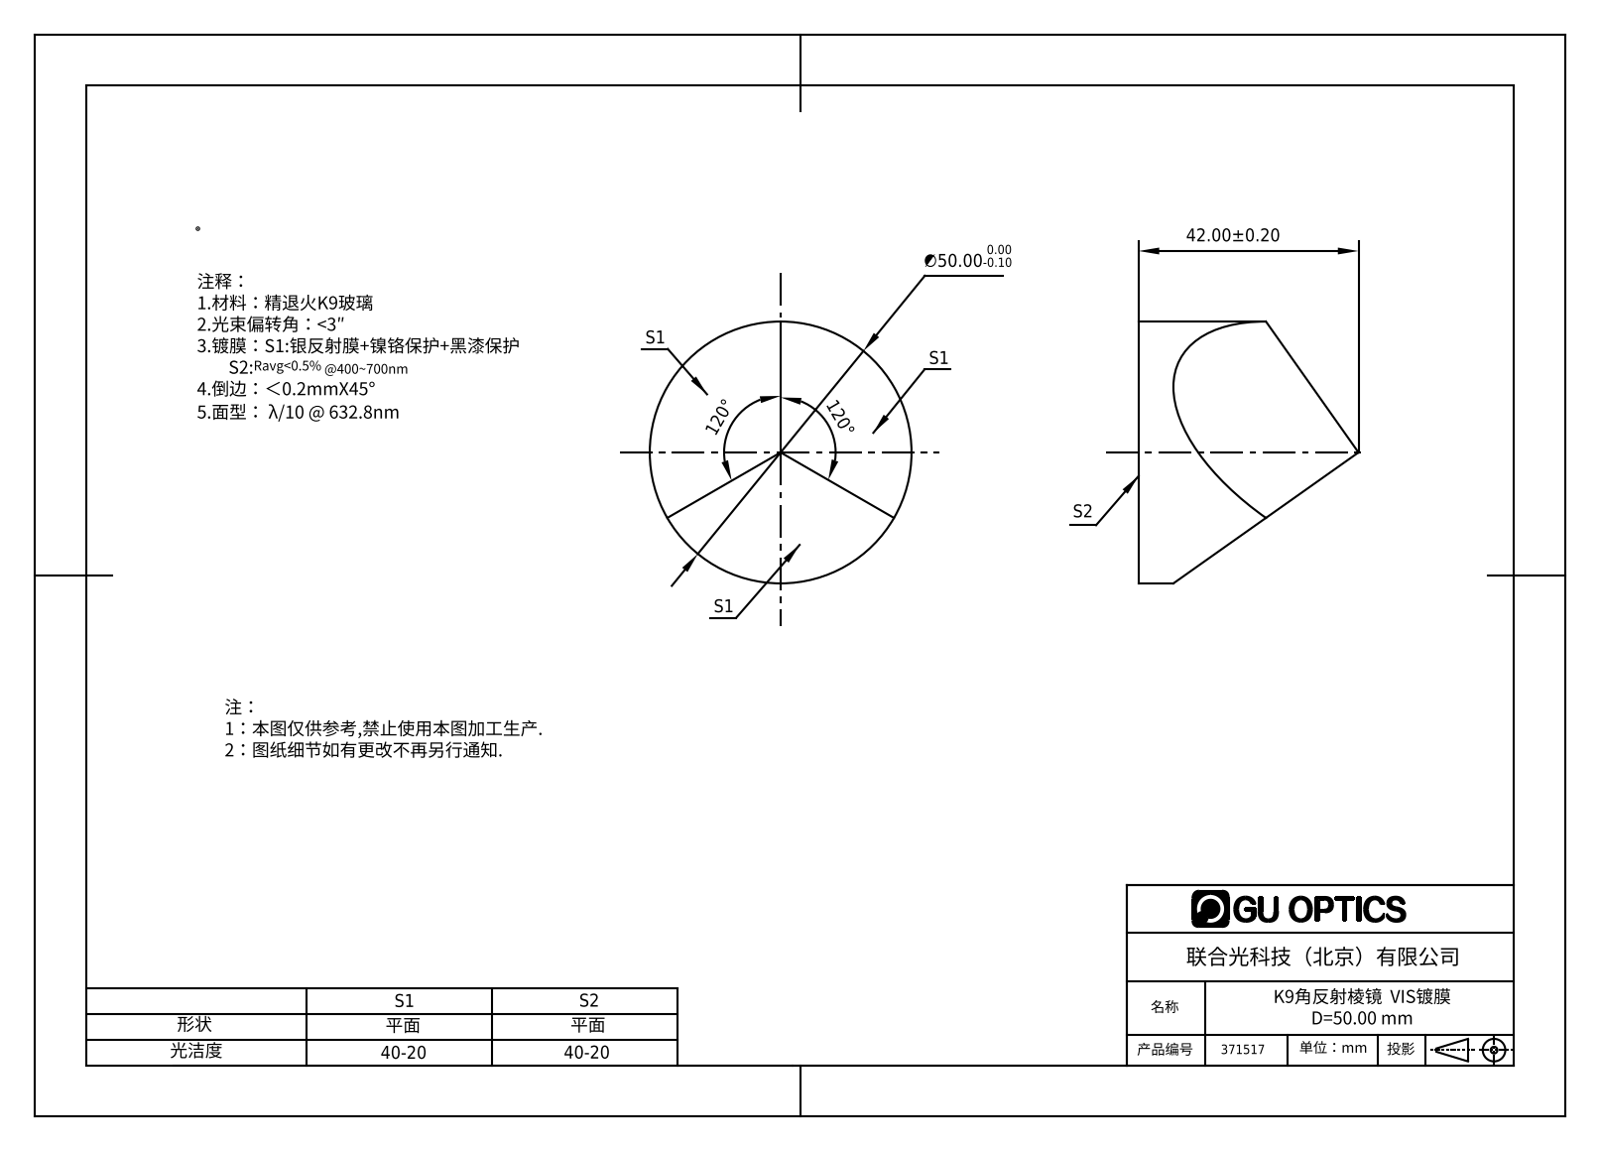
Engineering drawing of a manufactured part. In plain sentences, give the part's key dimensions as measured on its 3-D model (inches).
The part is named "371506". Its 3-D file was written by "SolidWorks 2016 (CONFIG_CONTROL_DESIGN)". It is 1 solid with 6 faces: 4 planar, 2 cylindrical and 0 other. Overall it measures 1.969 by 1.969 by 1.654 inches. Its volume is 2.697 cubic inches and its surface area 11.42 square inches. Round bosses or shafts: 1 of diameter 1.969.
